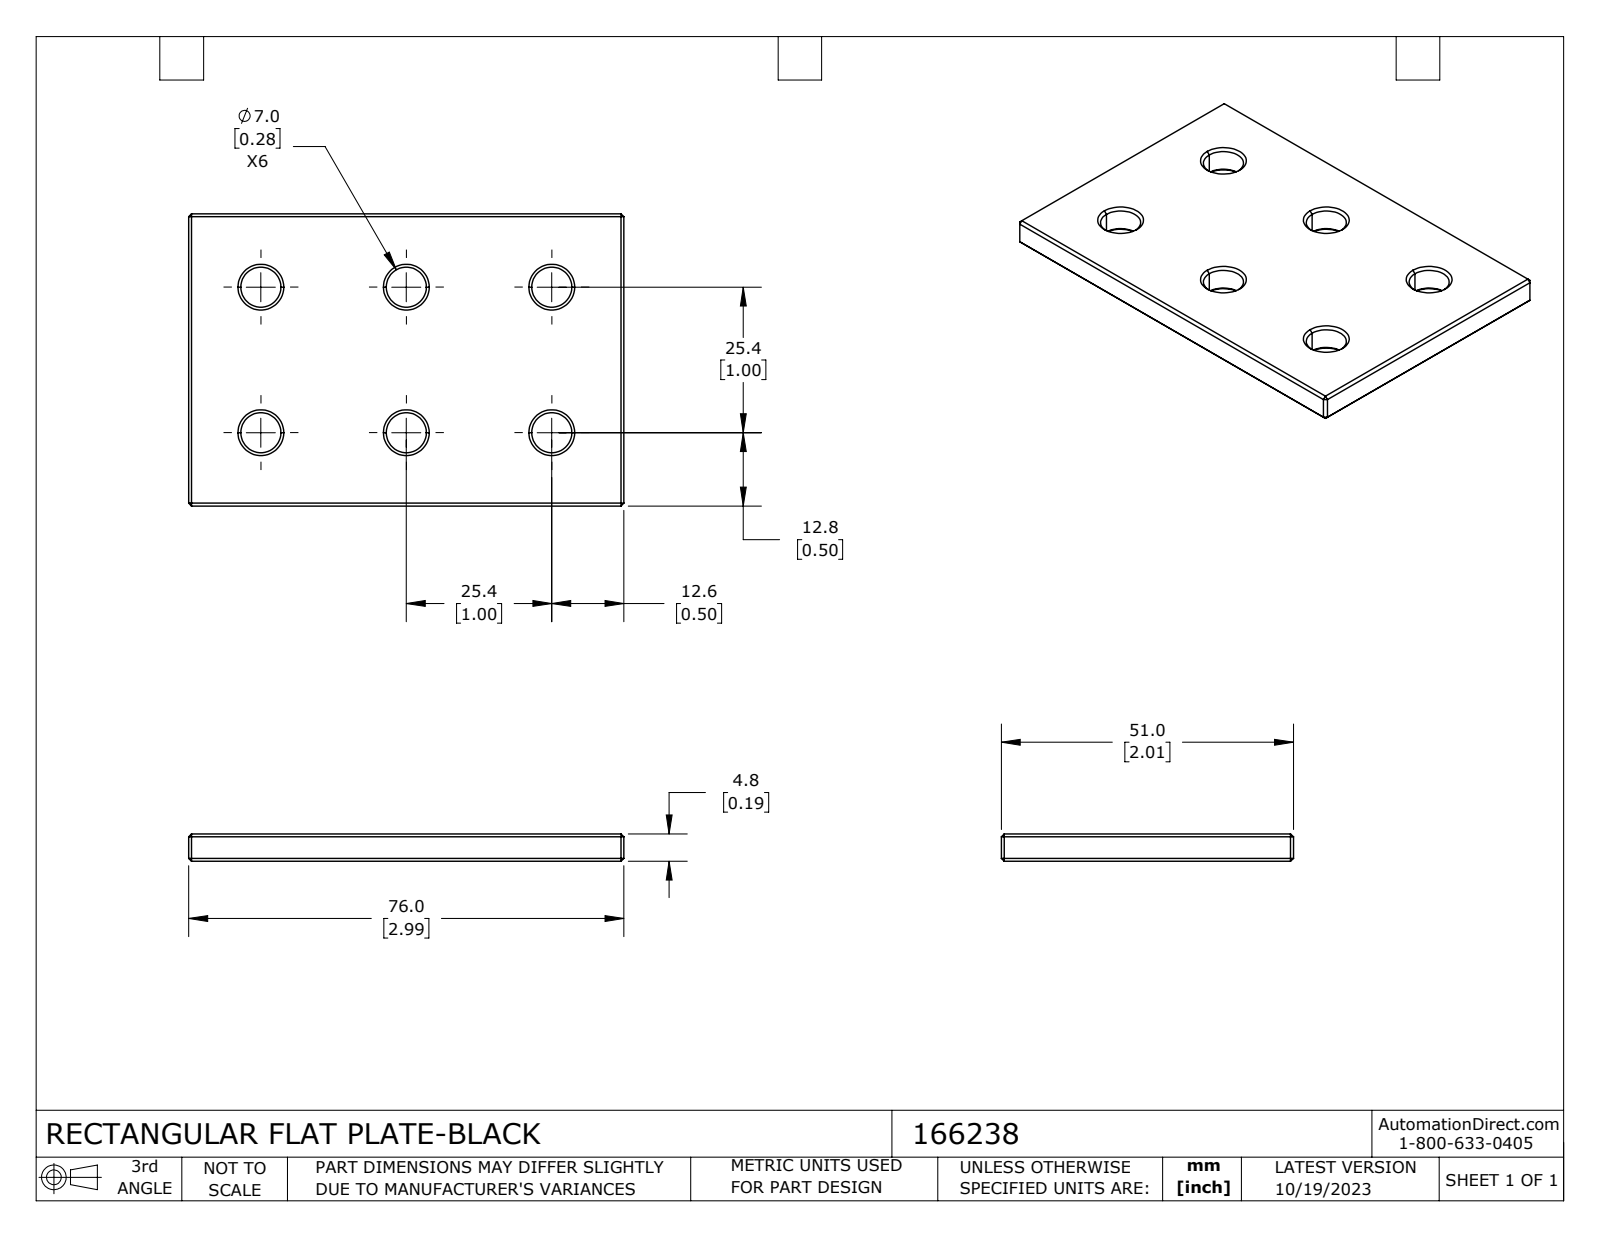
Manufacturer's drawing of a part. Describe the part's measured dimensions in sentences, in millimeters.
The part is named "166238". Its 3-D file was written by "SolidWorks 2023 (CONFIG_CONTROL_DESIGN)". It is 1 solid with 62 faces: 26 planar, 12 cylindrical and 24 other. Overall it measures 76 by 51 by 4.76 millimeters. Its volume is 17 260 cubic millimeters and its surface area 8 900 square millimeters. Round holes: 6 of diameter 7. The main face-to-face distances are 4.76, 51, 76, 38.71, 56.39, 89.08, 74.87. The hole center spacings are 25.4, 35.92, 50.8, 56.8.
